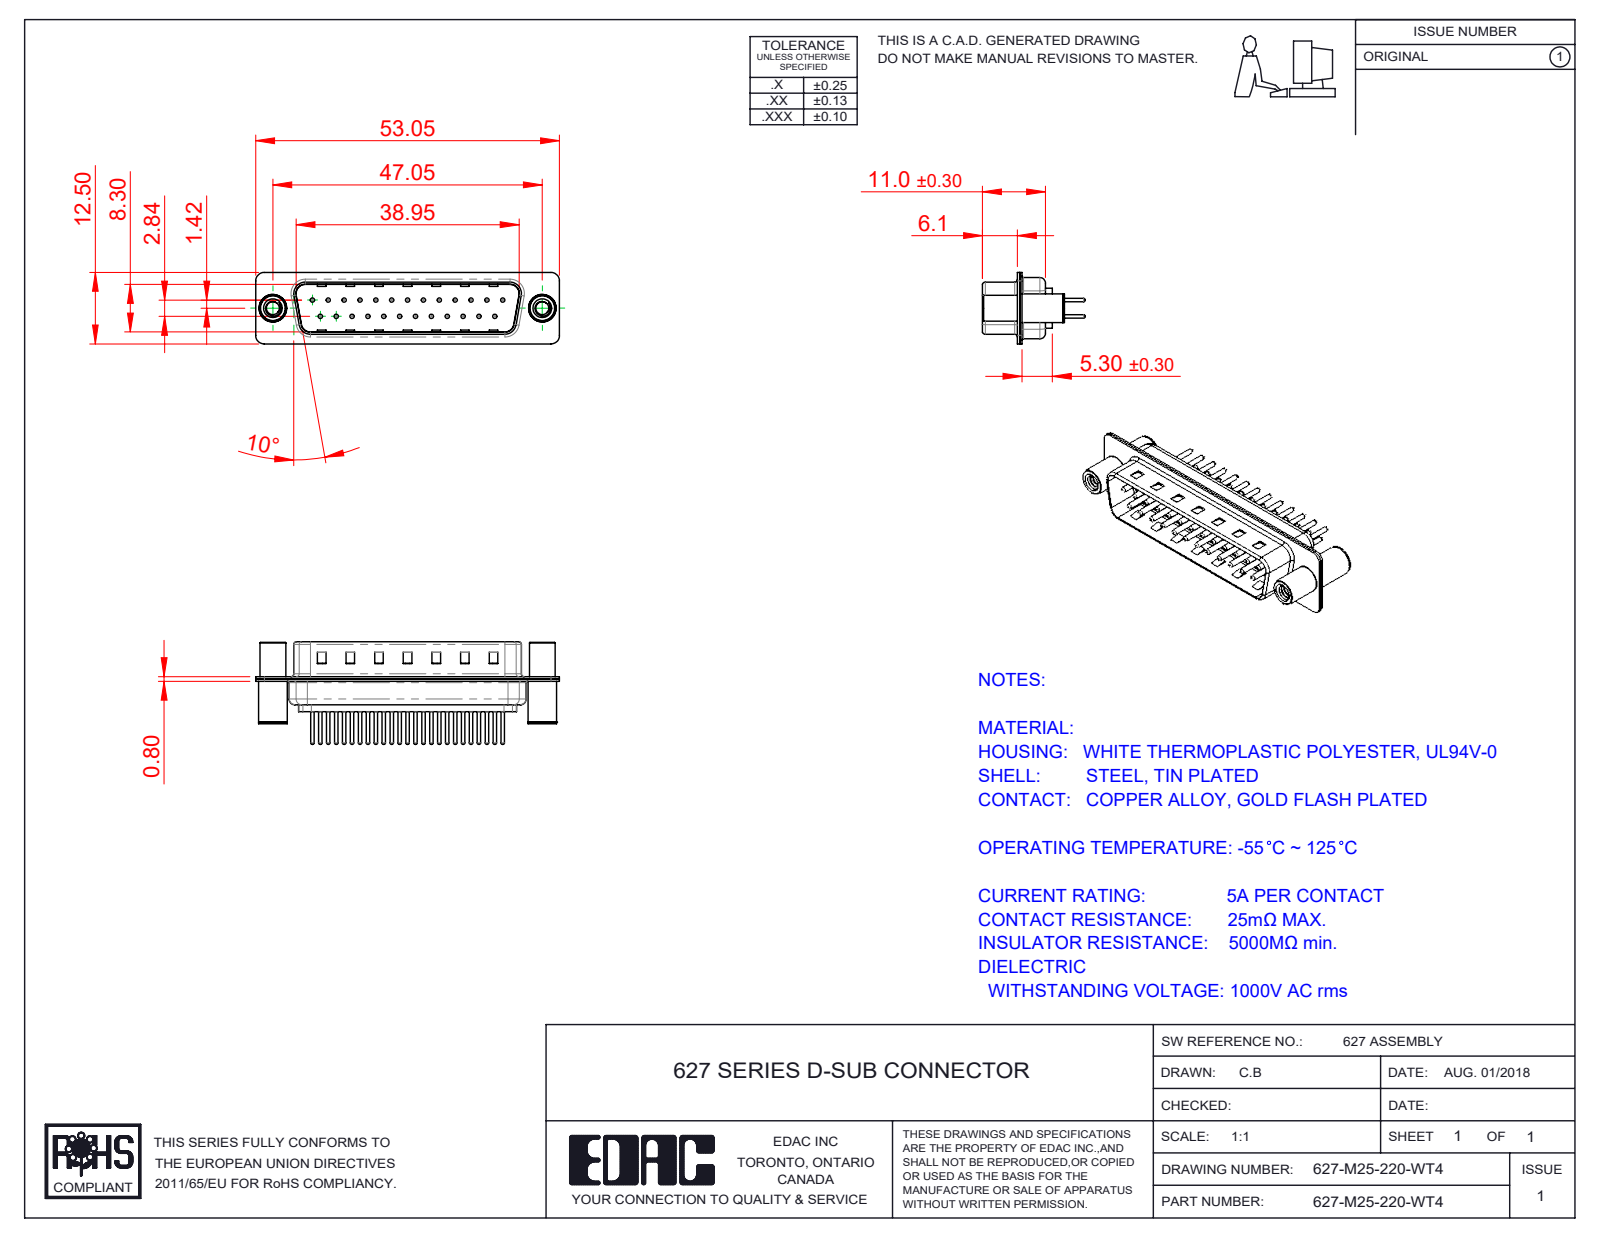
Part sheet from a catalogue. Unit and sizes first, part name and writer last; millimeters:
Units: millimetres
Overall size (bounding box): 53.05 × 17.9 × 12.5
Round holes (diameter × count): ⌀0.75 ×25, ⌀1.6 ×25, ⌀2 ×25, ⌀2.26 ×2, ⌀3.26 ×2, ⌀4 ×2, ⌀4.8 ×2
Round bosses / shafts (diameter × count): ⌀1.5 ×25, ⌀0.6 ×25, ⌀5 ×2, ⌀4.9 ×2, ⌀4.5 ×2
Partial cylindrical surfaces — rounded edges, fillets, slot ends (radius × count): R1.5 ×16, R2 ×12, R0.5 ×8, R1.6 ×8, R0.25 ×4, R0.6 ×4, R0.65 ×4, R0.9 ×4
Main face-to-face distances: 0.4, 0.8, 9.5, 9.1, 8.7, 9.9, 1.2, 5.7, 6.1, 0.75
Hole centre spacings: 3.16, 2.77, 5.54, 8.31, 11.08, 13.85, 16.62, 5.03
Volume: 3 006 mm³ · Surface area: 7 372 mm²
Bodies: 30 solids, 1387 faces (352 planar, 539 cylindrical, 496 other)
Part name (STEP PRODUCT): 627M Contact Row 1_20; 627M Shell Front_25 Contacts; 627M Shell Rear_25 Contacts; 627M 4-40 Threaded Standoff and Board Spacer (+3 more)
STEP written by: SolidWorks 2020 (CONFIG_CONTROL_DESIGN)
